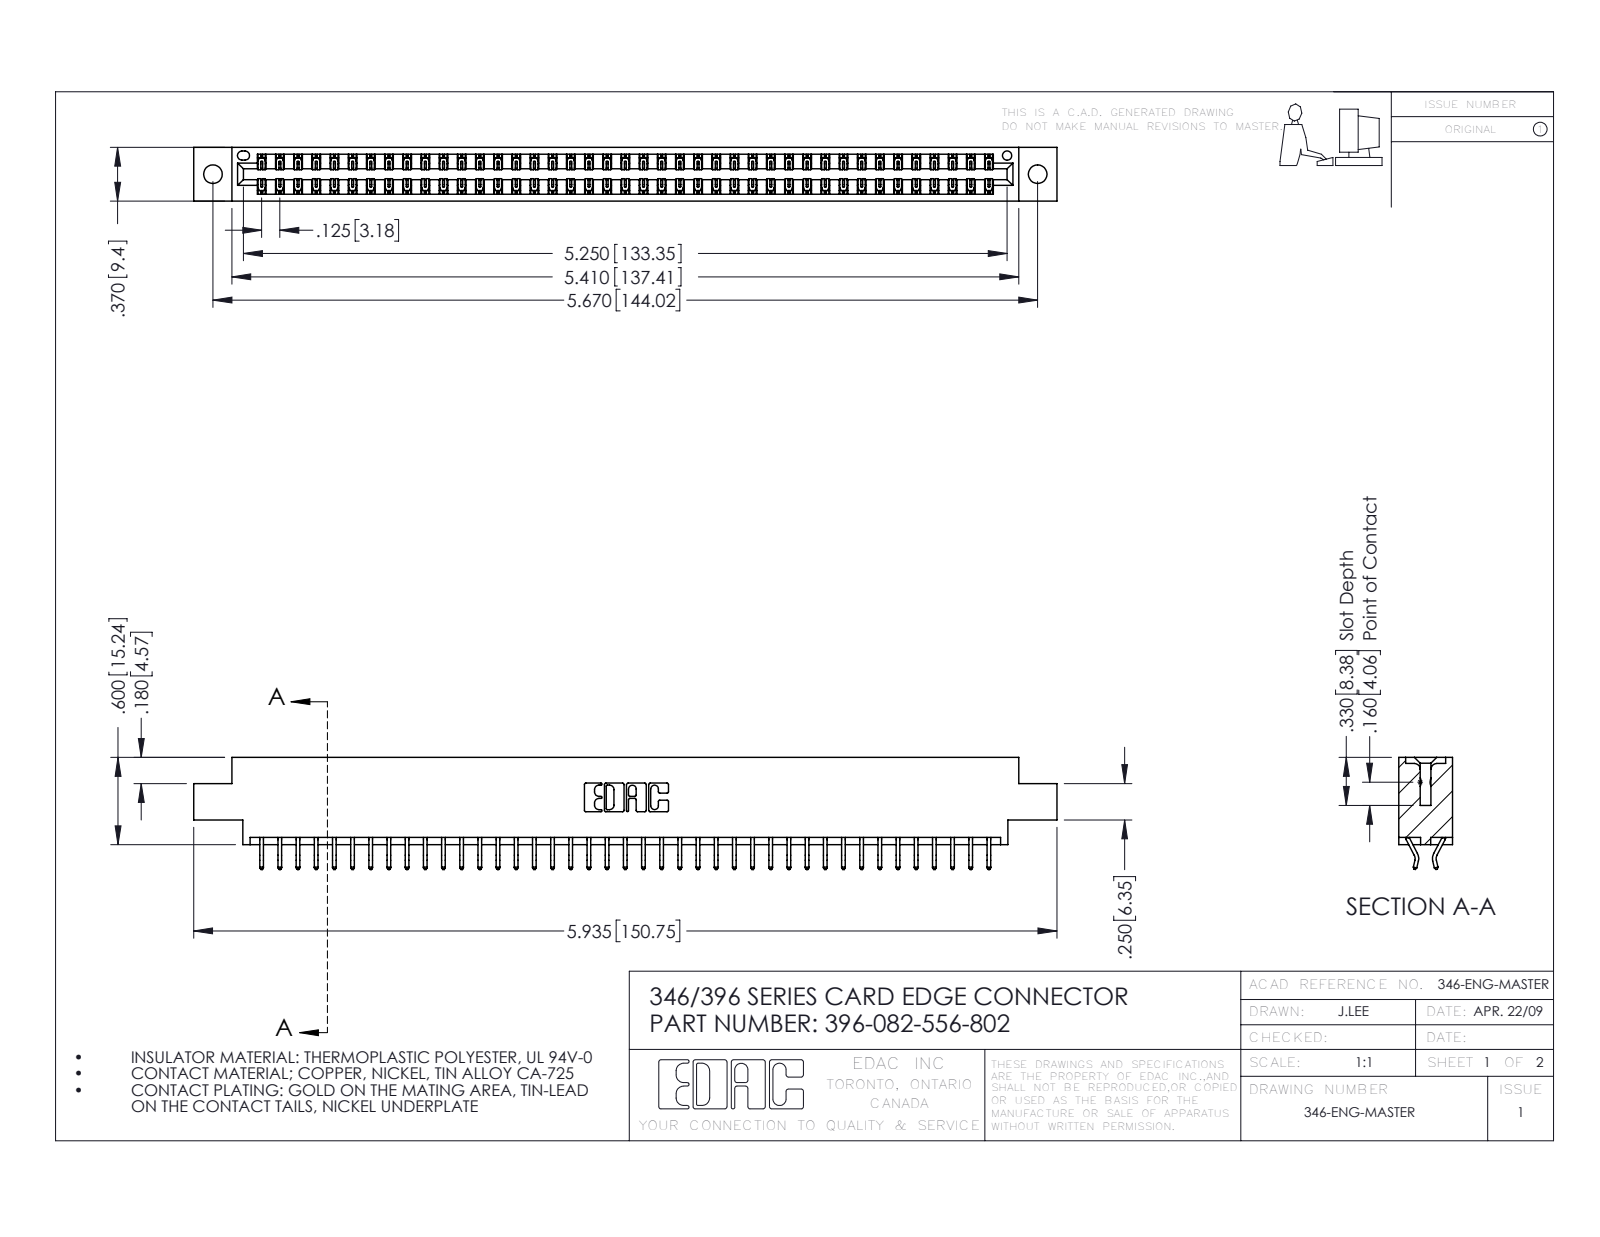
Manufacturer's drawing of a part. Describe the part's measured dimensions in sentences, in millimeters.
The part is named "396-082-556-802; 346 Part_0.170 Offset - 0.128 Dia; 345-292-001_556 Tail". Its 3-D file was written by "SolidWorks 2016 (CONFIG_CONTROL_DESIGN)". It is 83 solids with 4882 faces: 3278 planar, 1604 cylindrical and 0 other. Overall it measures 150.7 by 19.6 by 9.4 millimeters. Its volume is 14 500 cubic millimeters and its surface area 19 750 square millimeters. Round holes: 2 of diameter 3.3, 1 of diameter 1.6. Partial cylindrical surfaces (rounded edges, fillets, slot ends): 123 of radius 0.2, 22 of radius 0.3, 6 of radius 0.2, 6 of radius 0.8, 3 of radius 0.7, 2 of radius 0.3, 2 of radius 0.4, 2 of radius 0.6. The main face-to-face distances are 1.2, 8.2, 9.4, 6.4, 0.6, 1.8, 7.6, 7, 3.8, 5.6. The hole center spacings are 6.2, 138.7, 144.
